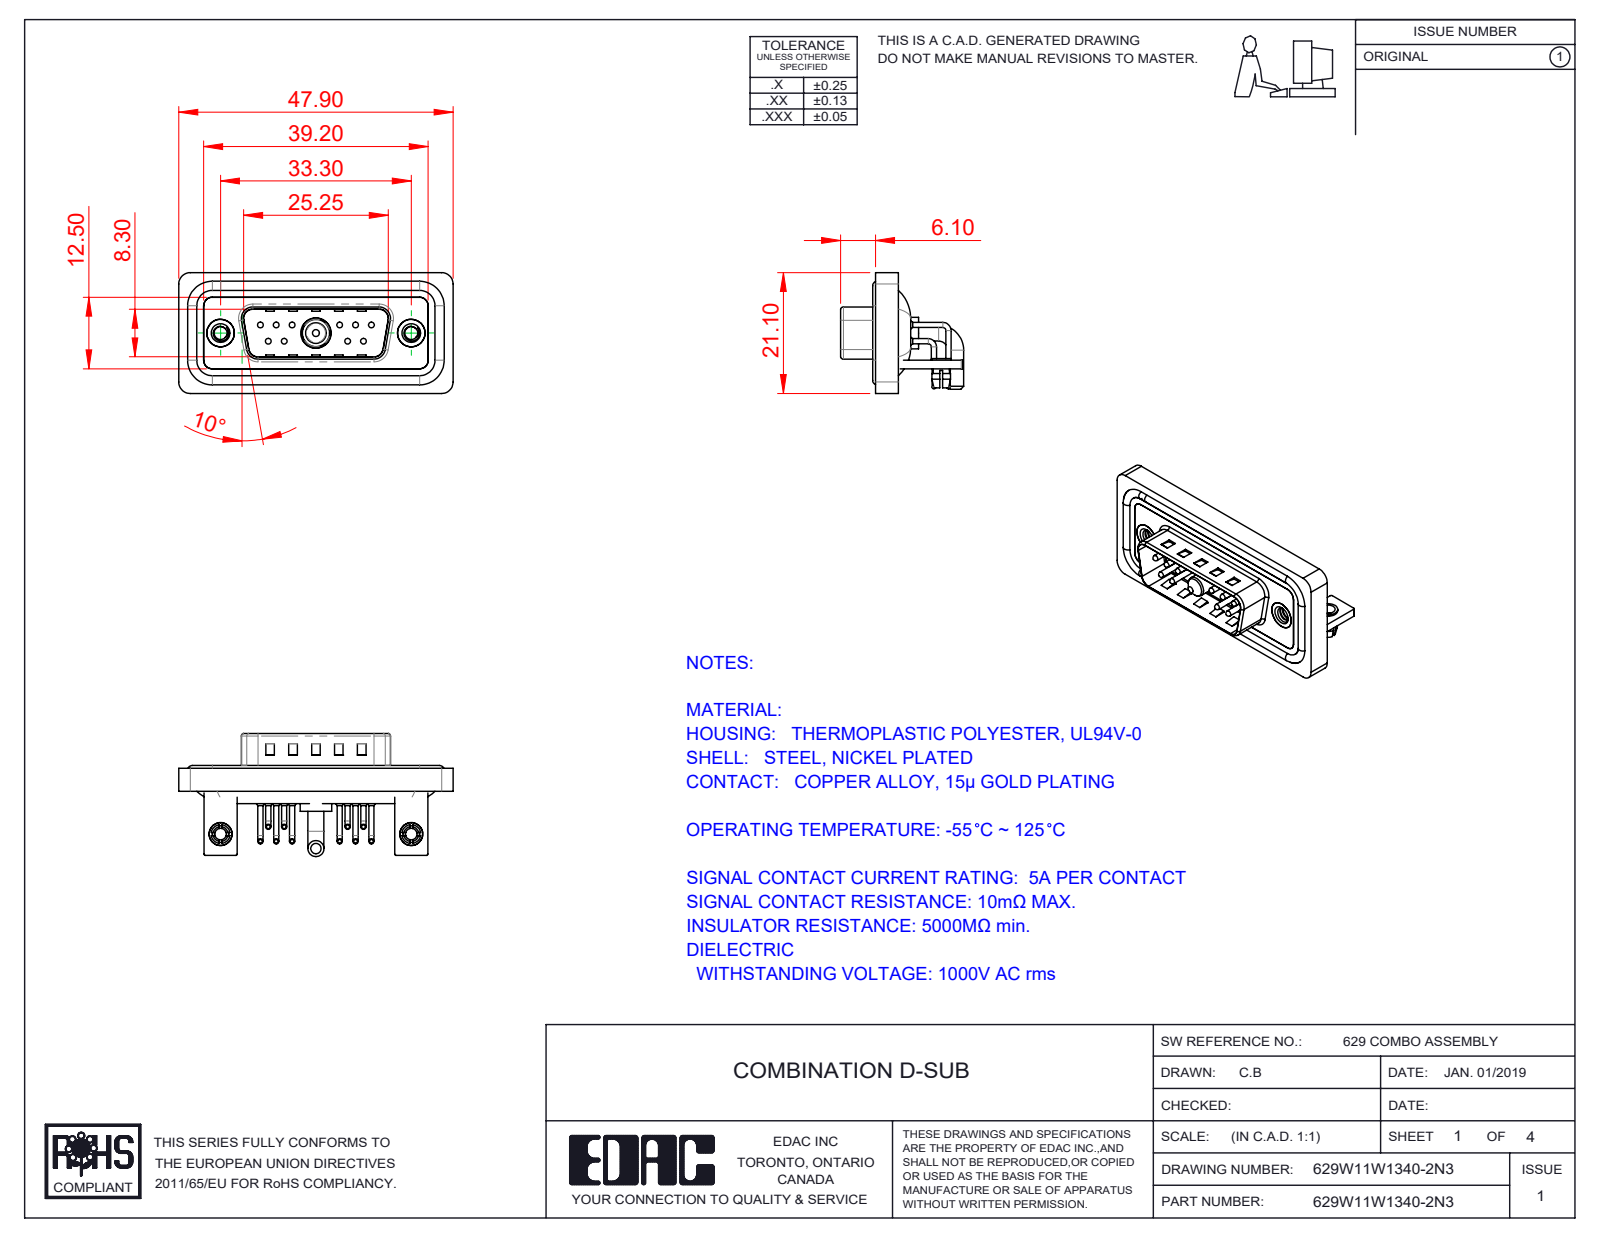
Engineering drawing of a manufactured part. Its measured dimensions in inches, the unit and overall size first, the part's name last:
Units: inches
Overall size (bounding box): 1.886 × 0.846 × 0.831
Round holes (diameter × count): ⌀0.079 ×12, ⌀0.03 ×10, ⌀0.063 ×10, ⌀0.089 ×2, ⌀0.098 ×2, ⌀0.126 ×2, ⌀0.157 ×2, ⌀0.189 ×2, ⌀0.197 ×2, ⌀0.191 ×1, ⌀0.209 ×1
Round bosses / shafts (diameter × count): ⌀0.035 ×20, ⌀0.059 ×10, ⌀0.039 ×10, ⌀0.026 ×10, ⌀0.063 ×4, ⌀0.193 ×2, ⌀0.157 ×2, ⌀0.134 ×2
Partial cylindrical surfaces — rounded edges, fillets, slot ends (radius × count): R0.079 ×21, R0.059 ×18, R0.01 ×16, R0.04 ×10, R0.02 ×9, R0.063 ×8, R0.039 ×7, R0.024 ×4
Main face-to-face distances: 0.016, 0.031, 0.059, 0.114, 0.083, 0.043, 0.063, 0.047, 0.146, 0.161
Hole centre spacings: 0.124, 0.109, 0.545, 0.436, 0.654, 0.198, 0.198, 0.218
Volume: 0.36 in³ · Surface area: 15.62 in²
Bodies: 23 solids, 1735 faces (904 planar, 619 cylindrical, 212 other)
Part name (STEP PRODUCT): 629Combo Threaded Rivet_3; 629Combo Shell Front_15 Contacts; 629Combo Contact Row 2; 629Combo Housing_11W1 (+7 more)
STEP written by: SolidWorks 2023 (CONFIG_CONTROL_DESIGN)
